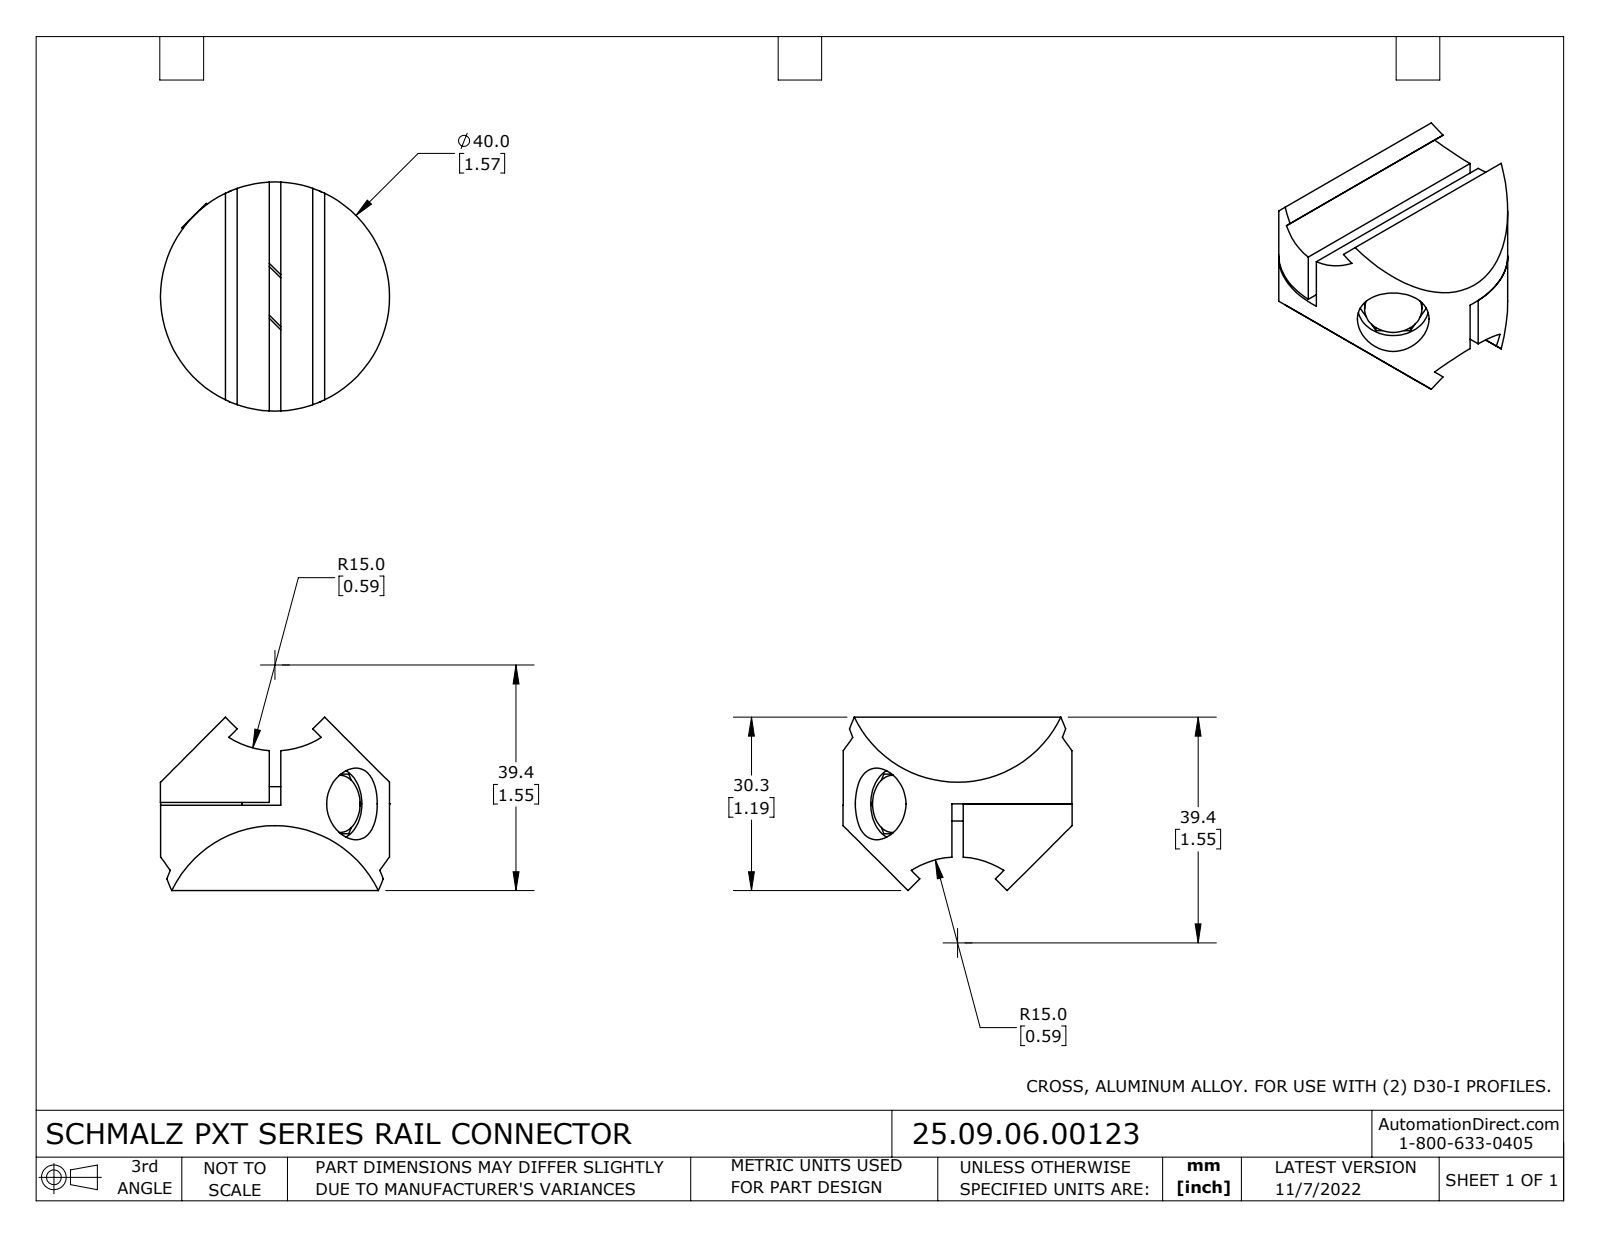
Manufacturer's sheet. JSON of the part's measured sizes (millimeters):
{"part_name": "25.09.06.00123", "step_written_by": "SolidWorks 2021 (CONFIG_CONTROL_DESIGN)", "units": "millimeters", "bodies": {"solids": 4, "faces": 69, "planar": 47, "cylindrical": 22, "other": 0}, "overall_size": [40, 40, 30.27], "volume_mm3": 23715, "surface_area_mm2": 10519, "round_holes": [[5, 1], [6.8, 1], [12.5, 1]], "round_bosses_or_shafts": [[40, 1], [10, 1], [6, 1]], "partial_cylinders_radius": [[15, 2]], "face_to_face_distances": [2, 12.23, 9.33, 2.9, 0.5, 5.2, 25.2, 4.95, 5.45, 10.39]}
